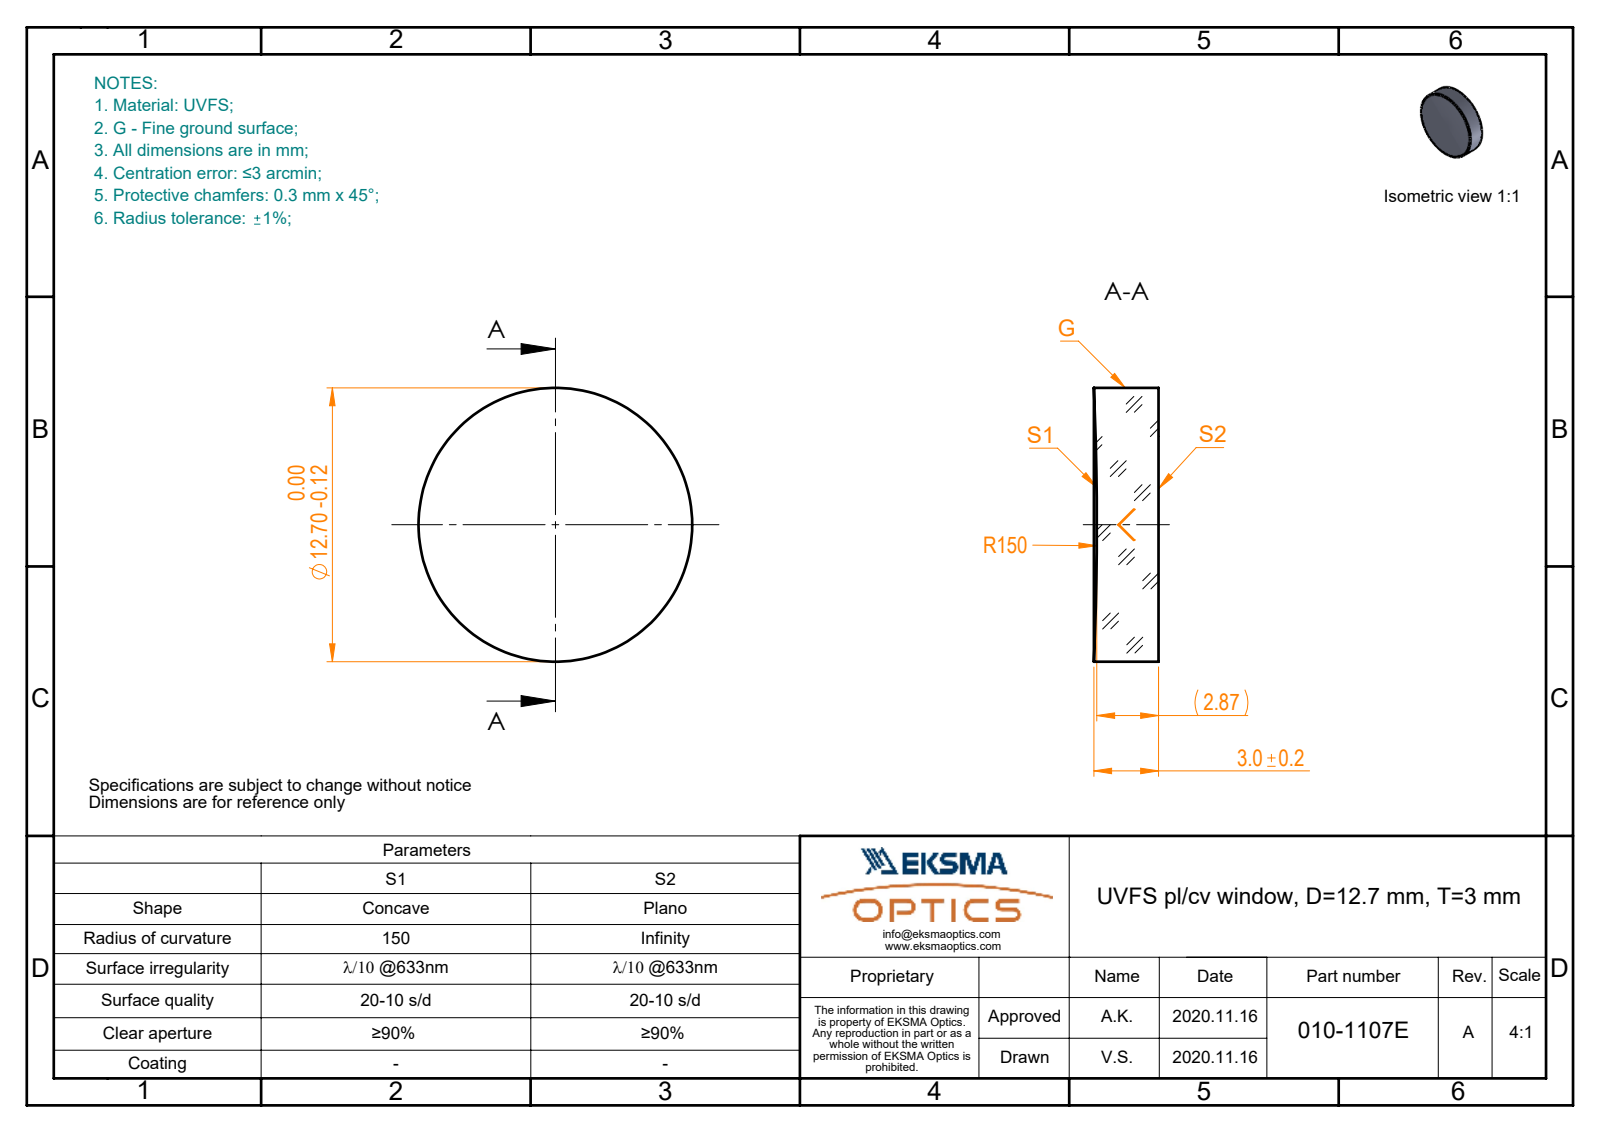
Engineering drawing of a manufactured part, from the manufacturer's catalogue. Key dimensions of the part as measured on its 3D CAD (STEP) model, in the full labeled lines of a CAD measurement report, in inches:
Part name (STEP PRODUCT): 010-1107E_UVFS_PCV_window
STEP written by: SolidWorks 2019 (CONFIG_CONTROL_DESIGN)
Units: inches
Bodies: 1 solid, 5 faces (1 planar, 2 cylindrical, 2 other)
Overall size (bounding box): 0.5 × 0.5 × 0.118
Volume: 0.023 in³ · Surface area: 0.578 in²
Round bosses / shafts (diameter × count): ⌀0.5 ×1
